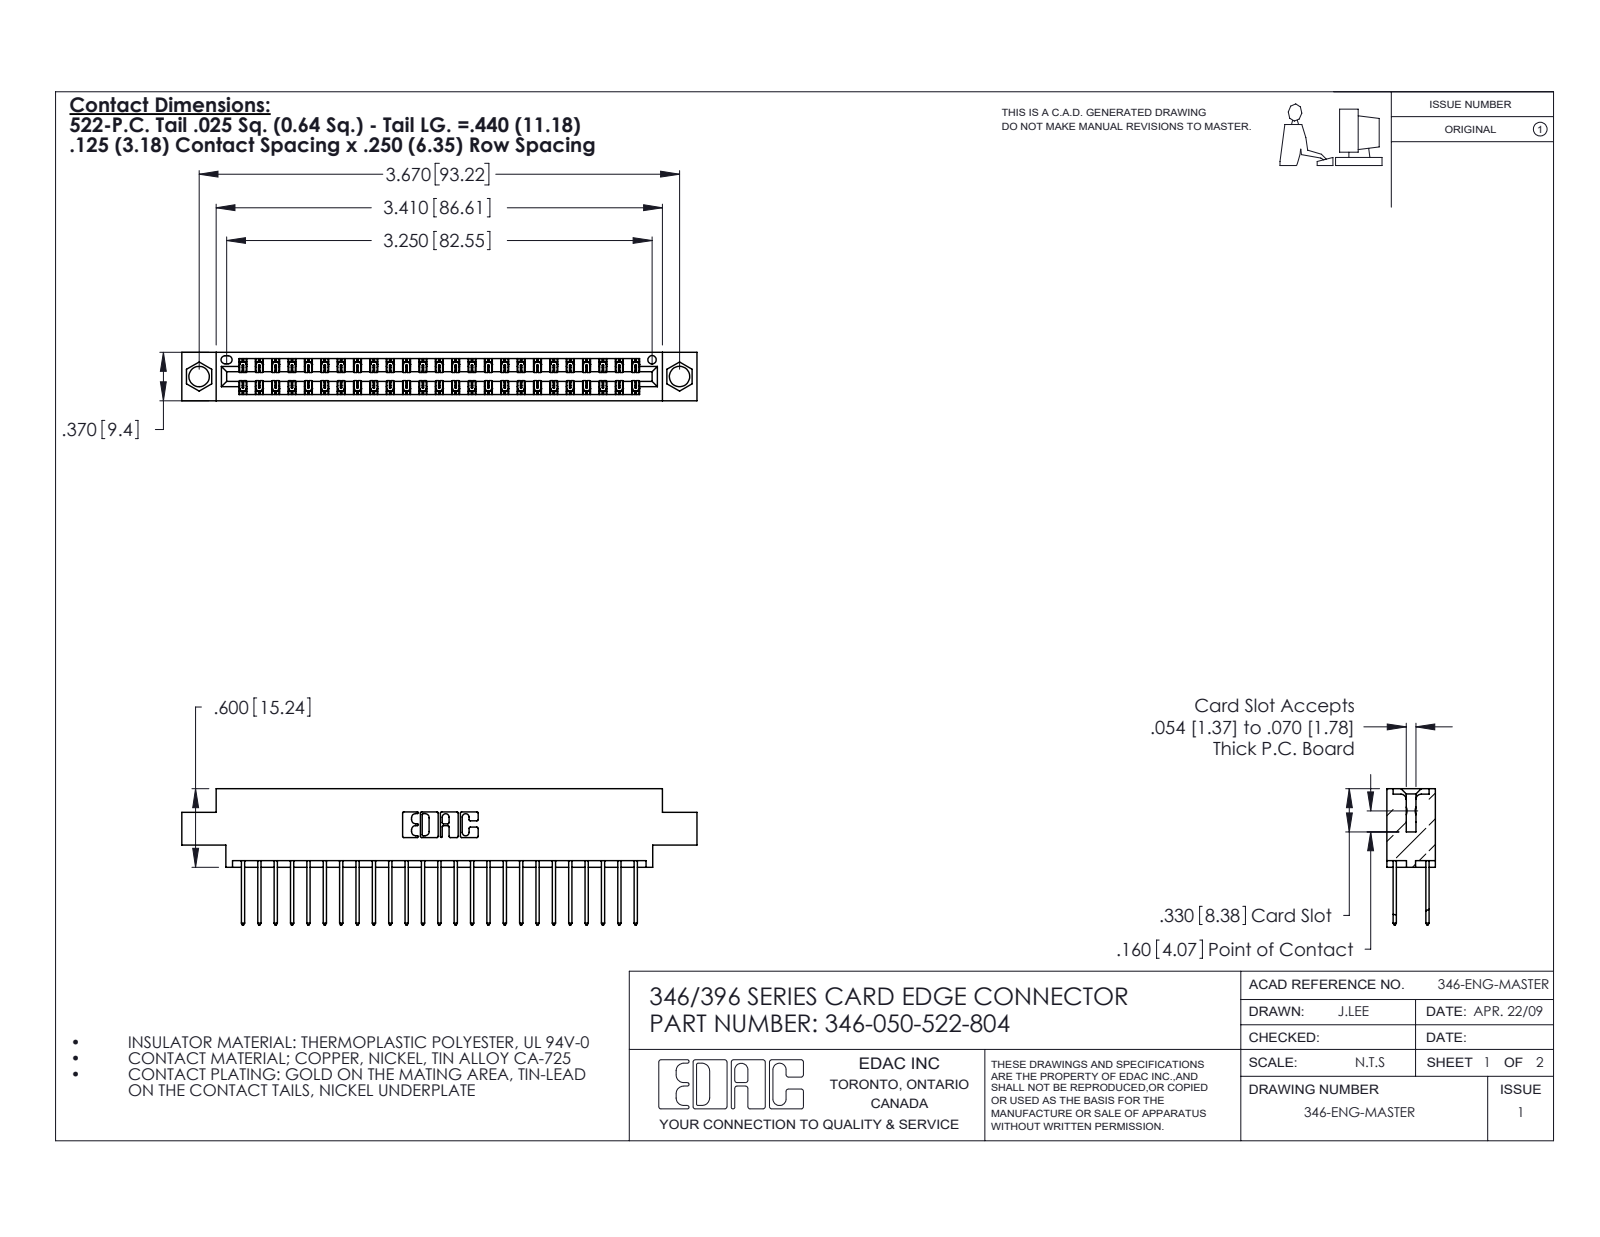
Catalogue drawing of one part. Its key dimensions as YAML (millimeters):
part_name: "346 Part_0.170 Offset - 0.156 Dia-TH; 345-292-001_345-293-122; 346-050-522-804"
step_written_by: "SolidWorks 2020 (CONFIG_CONTROL_DESIGN)"
units: millimeters
bodies: {solids: 51, faces: 2740, planar: 1844, cylindrical: 896, other: 0}
overall_size: [99.9, 26.4, 9.4]
volume: 9490
surface_area: 13390
round_holes:
  - {diameter: 4, count: 2}
  - {diameter: 1.6, count: 1}
partial_cylinders:
  - {radius: 0.2, count: 75}
  - {radius: 0.3, count: 50}
  - {radius: 0.3, count: 22}
  - {radius: 0.2, count: 6}
  - {radius: 0.8, count: 6}
  - {radius: 0.7, count: 3}
  - {radius: 0.4, count: 2}
  - {radius: 0.6, count: 2}
face_to_face_distances: [1.2, 8.2, 6.4, 9.4, 1.8, 7.6, 0.6, 7, 5.6, 3.8]
hole_center_spacings: [6.2, 87.9, 93.2]
